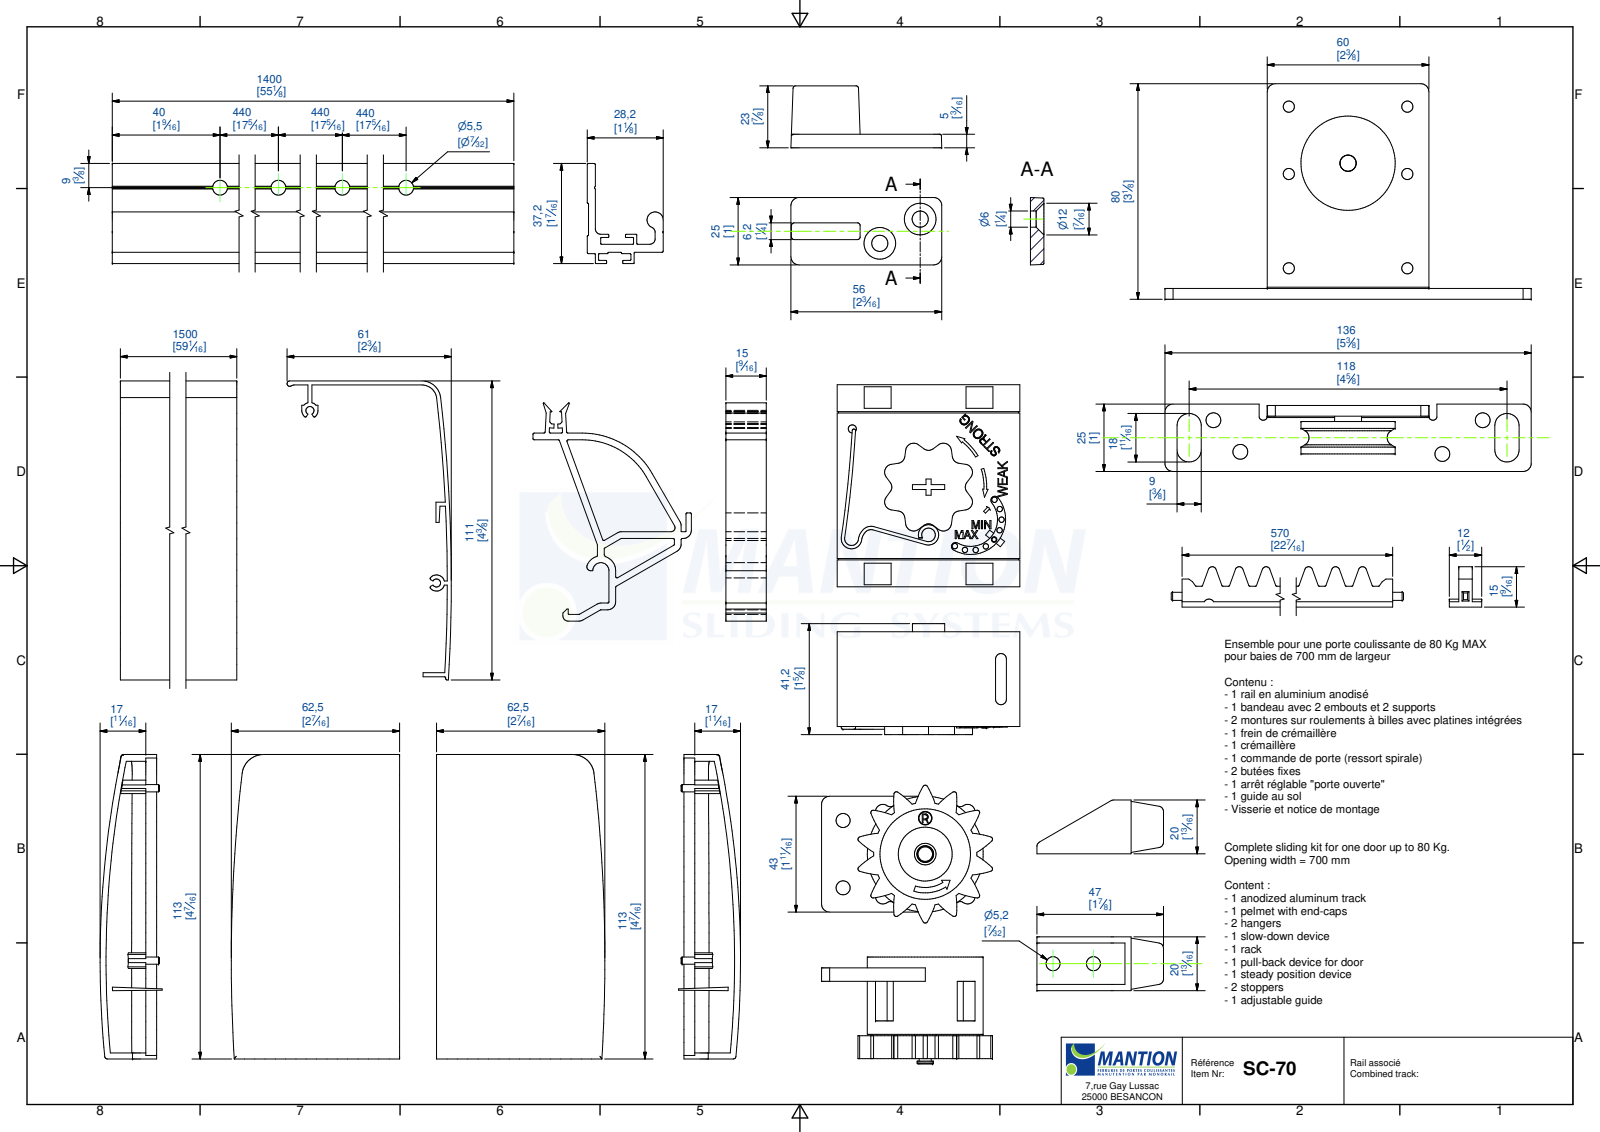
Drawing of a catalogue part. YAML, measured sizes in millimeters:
part_name: "Ferme porte meca-45mm-version cale bois MDF; 21592; 21580; 21577 (+8 more)"
step_written_by: "Autodesk Inventor 2019 (AUTOMOTIVE_DESIGN)"
units: millimeters
bodies: {solids: 75, faces: 3498, planar: 2074, cylindrical: 1005, other: 419}
overall_size: [2167.38, 1534, 84.5]
volume: 1281000
surface_area: 1137000
round_holes:
  - {diameter: 2, count: 20}
  - {diameter: 4.13, count: 14}
  - {diameter: 5.5, count: 12}
  - {diameter: 5.2, count: 6}
  - {diameter: 6, count: 6}
  - {diameter: 5.3, count: 5}
  - {diameter: 4.3, count: 4}
  - {diameter: 3, count: 3}
  - {diameter: 2.46, count: 2}
  - {diameter: 3.2, count: 2}
  - {diameter: 3.24, count: 2}
  - {diameter: 4.2, count: 2}
round_bosses_or_shafts:
  - {diameter: 4.5, count: 13}
  - {diameter: 8.75, count: 12}
  - {diameter: 5, count: 8}
  - {diameter: 10, count: 7}
  - {diameter: 4, count: 5}
  - {diameter: 9, count: 4}
  - {diameter: 4.8, count: 4}
  - {diameter: 35, count: 2}
partial_cylinders:
  - {radius: 0.5, count: 175}
  - {radius: 1.5, count: 64}
  - {radius: 3, count: 61}
  - {radius: 2, count: 53}
  - {radius: 0.3, count: 32}
  - {radius: 33, count: 28}
  - {radius: 1, count: 21}
  - {radius: 0.9, count: 14}
face_to_face_distances: [1.5, 3, 0.5, 2.5, 75.5, 77, 108.3, 28.2, 25.2, 5]
hole_center_spacings: [530, 44, 22.36, 25, 30.41, 35, 44.78, 50.56]
